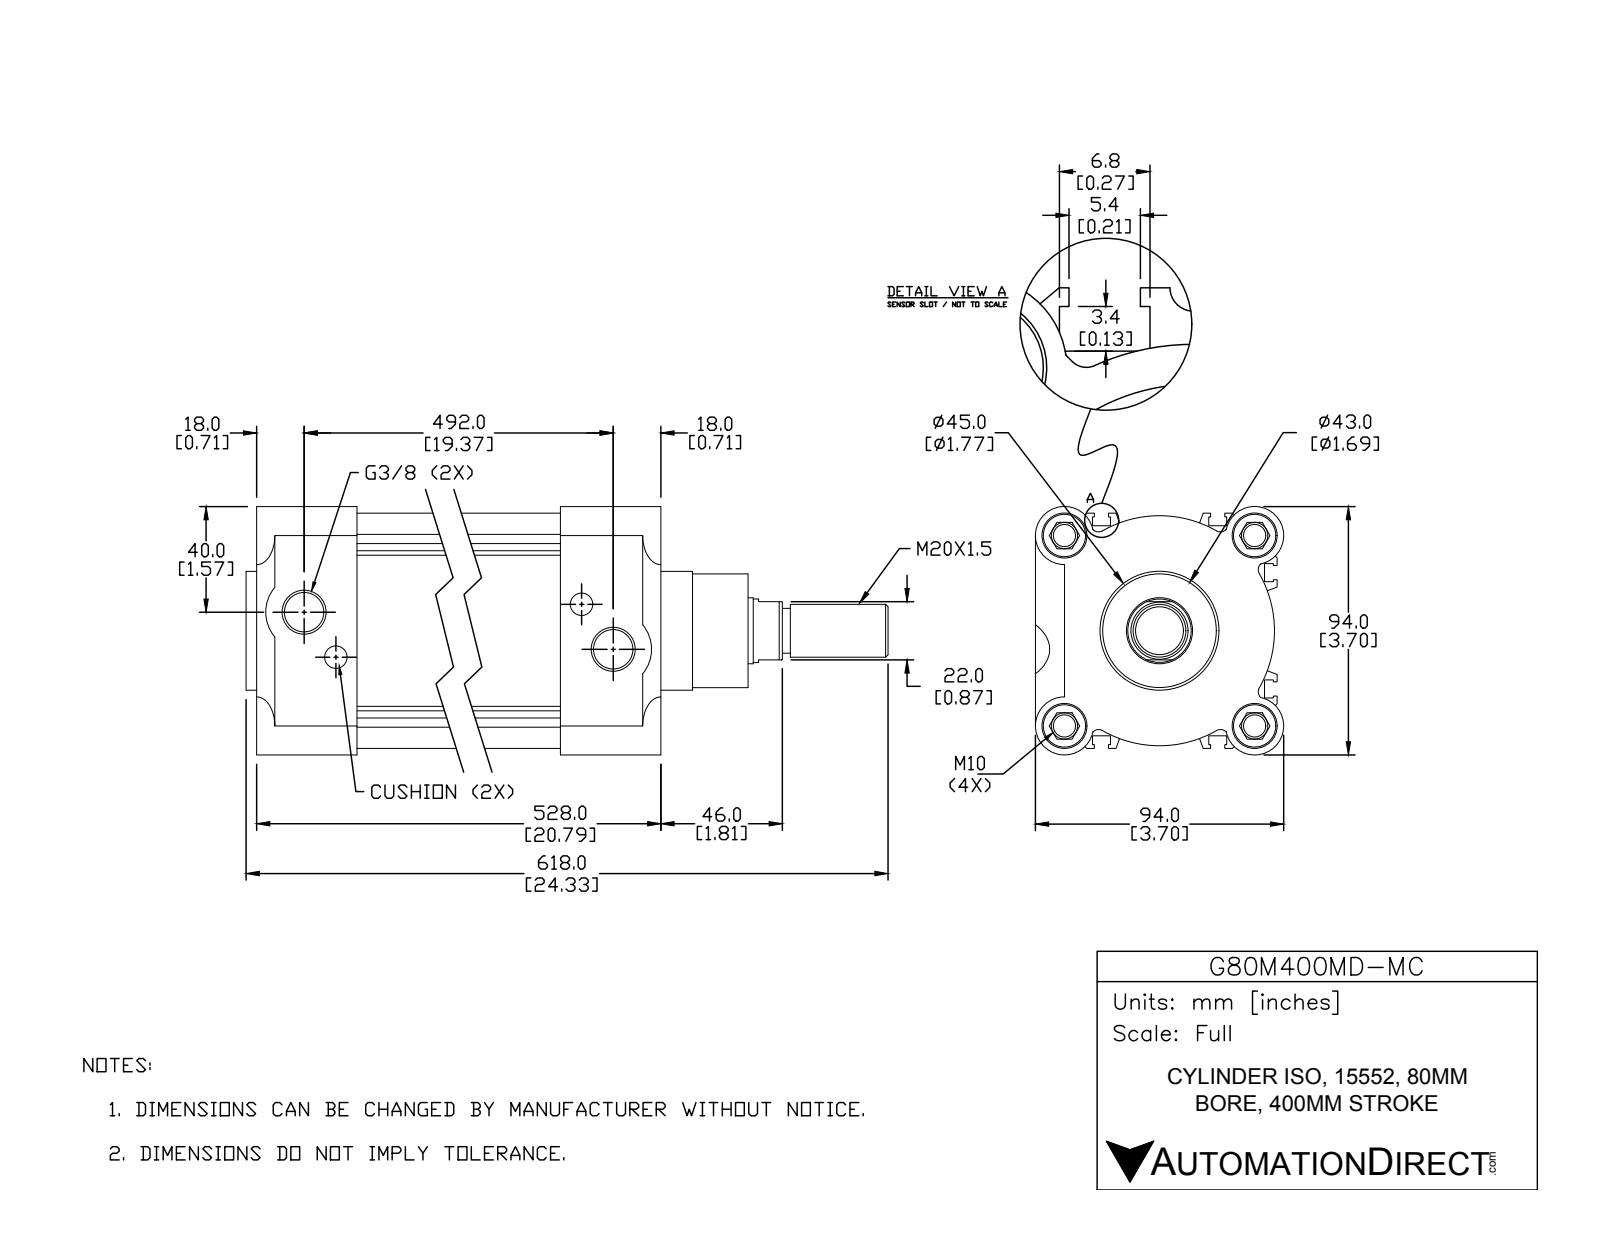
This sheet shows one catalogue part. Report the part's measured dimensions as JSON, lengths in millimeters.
{"part_name": "80121-HR; 80-HL; 80-400-110.5-B; G80M400MD-MC (+1 more)", "step_written_by": "SolidWorks 2015 (CONFIG_CONTROL_DESIGN)", "units": "millimeters", "bodies": {"solids": 4, "faces": 418, "planar": 236, "cylindrical": 138, "other": 44}, "overall_size": [618, 94, 94], "volume_mm3": 2134000, "surface_area_mm2": 486800, "round_holes": [[8.4, 4], [17, 4], [8.5, 2], [15, 2], [25, 1]], "round_bosses_or_shafts": [[16, 4], [80, 1], [45, 1], [43, 1], [24, 1], [20, 1], [17, 1]], "partial_cylinders_radius": [[0.1, 6], [3, 6], [8, 4], [11, 4], [14.5, 2], [43, 1], [43.5, 1]], "face_to_face_distances": [4.7, 84.3, 42.8, 59.1, 89, 10, 44, 442, 38, 490], "hole_center_spacings": [50.9, 72, 20.8, 101.8, 480, 468.4, 492.2]}
